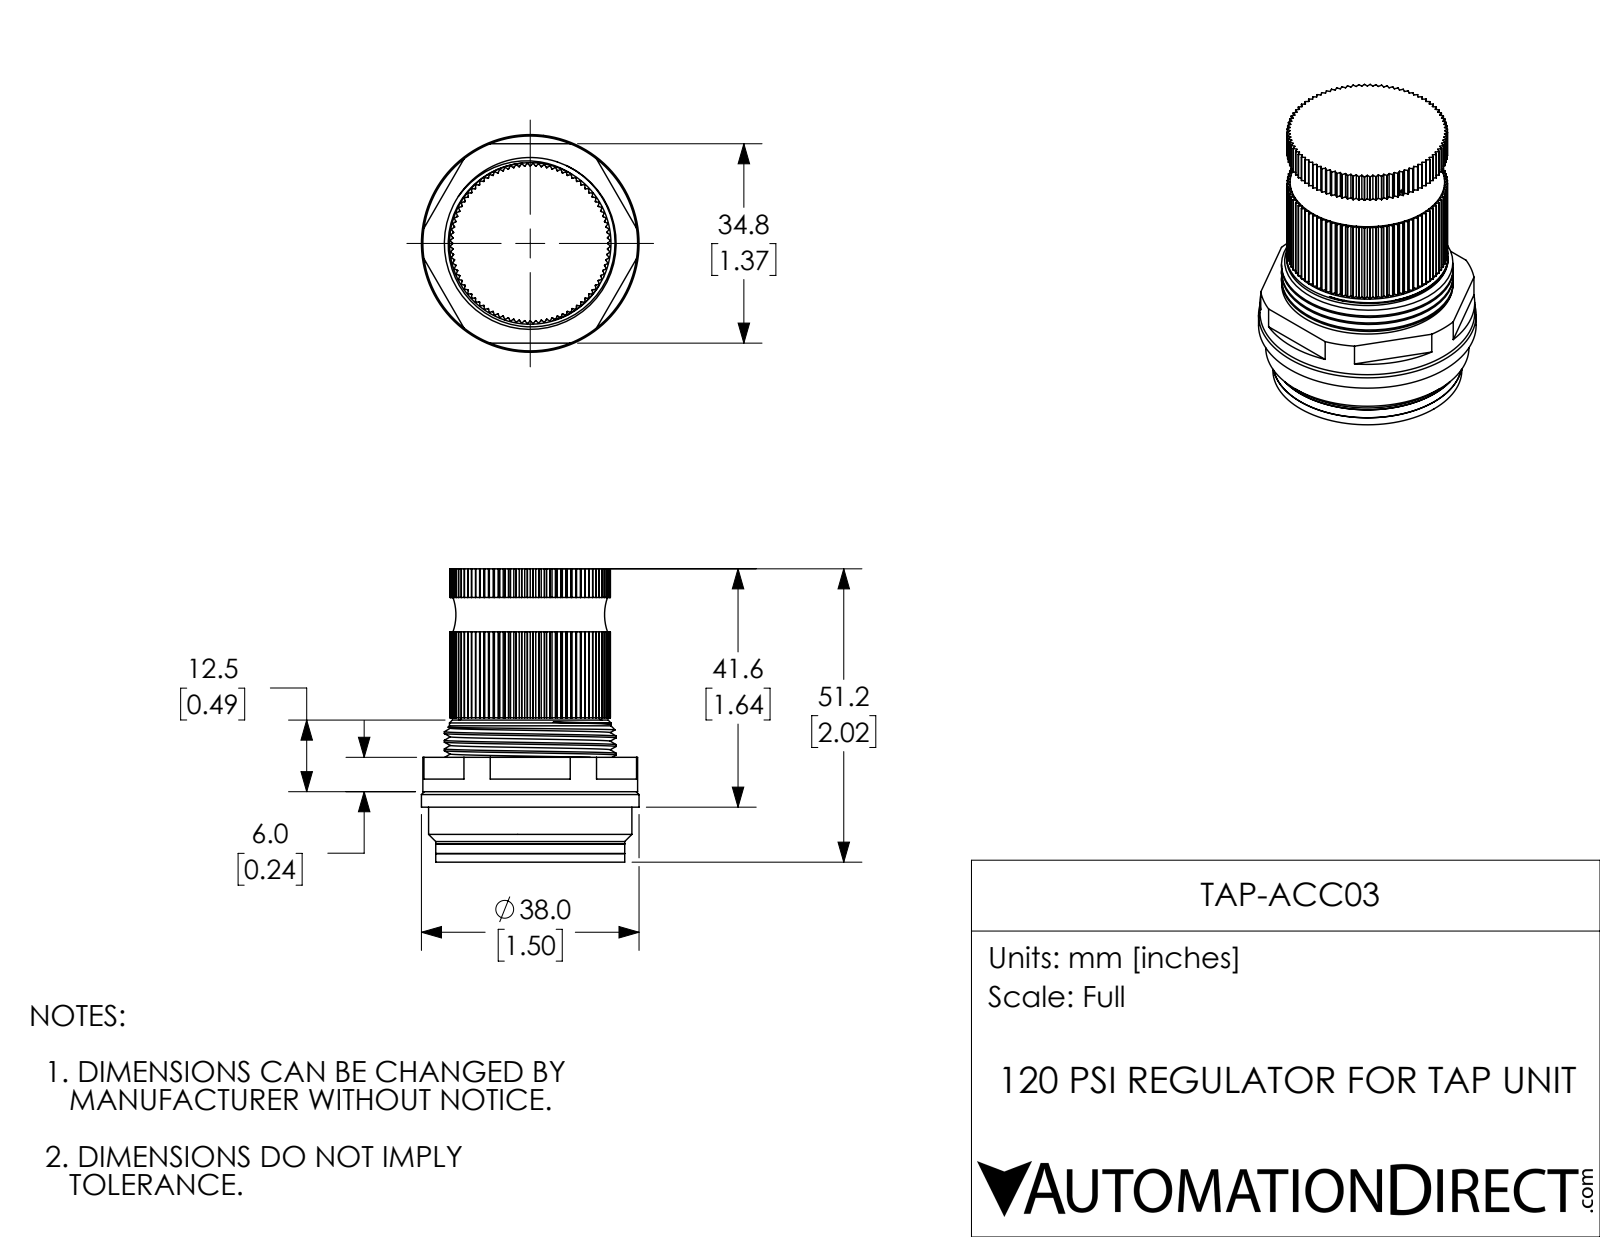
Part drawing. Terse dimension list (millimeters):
name: TAP-ACC03
written by: SolidWorks 2017 (AUTOMOTIVE_DESIGN)
unit: mm
bodies: 8 solids, 713 faces (435 planar, 247 cylindrical, 31 other)
size: 51.2 × 38 × 38
volume: 28 089 mm³; area: 25 001 mm²
holes: 1× ⌀12, 1× ⌀18.6, 1× ⌀22, 1× ⌀24, 1× ⌀26.5, 1× ⌀27, 1× ⌀29.9
bosses: 1× ⌀38, 1× ⌀37.5, 1× ⌀35.5, 1× ⌀33, 1× ⌀30, 1× ⌀28.2, 1× ⌀22.2, 1× ⌀16.8
rounds: 1× R14
face distances: 9.1, 19.09, 10.8, 1.7, 38.7, 37, 27.9, 38.9, 19.1, 19.08
